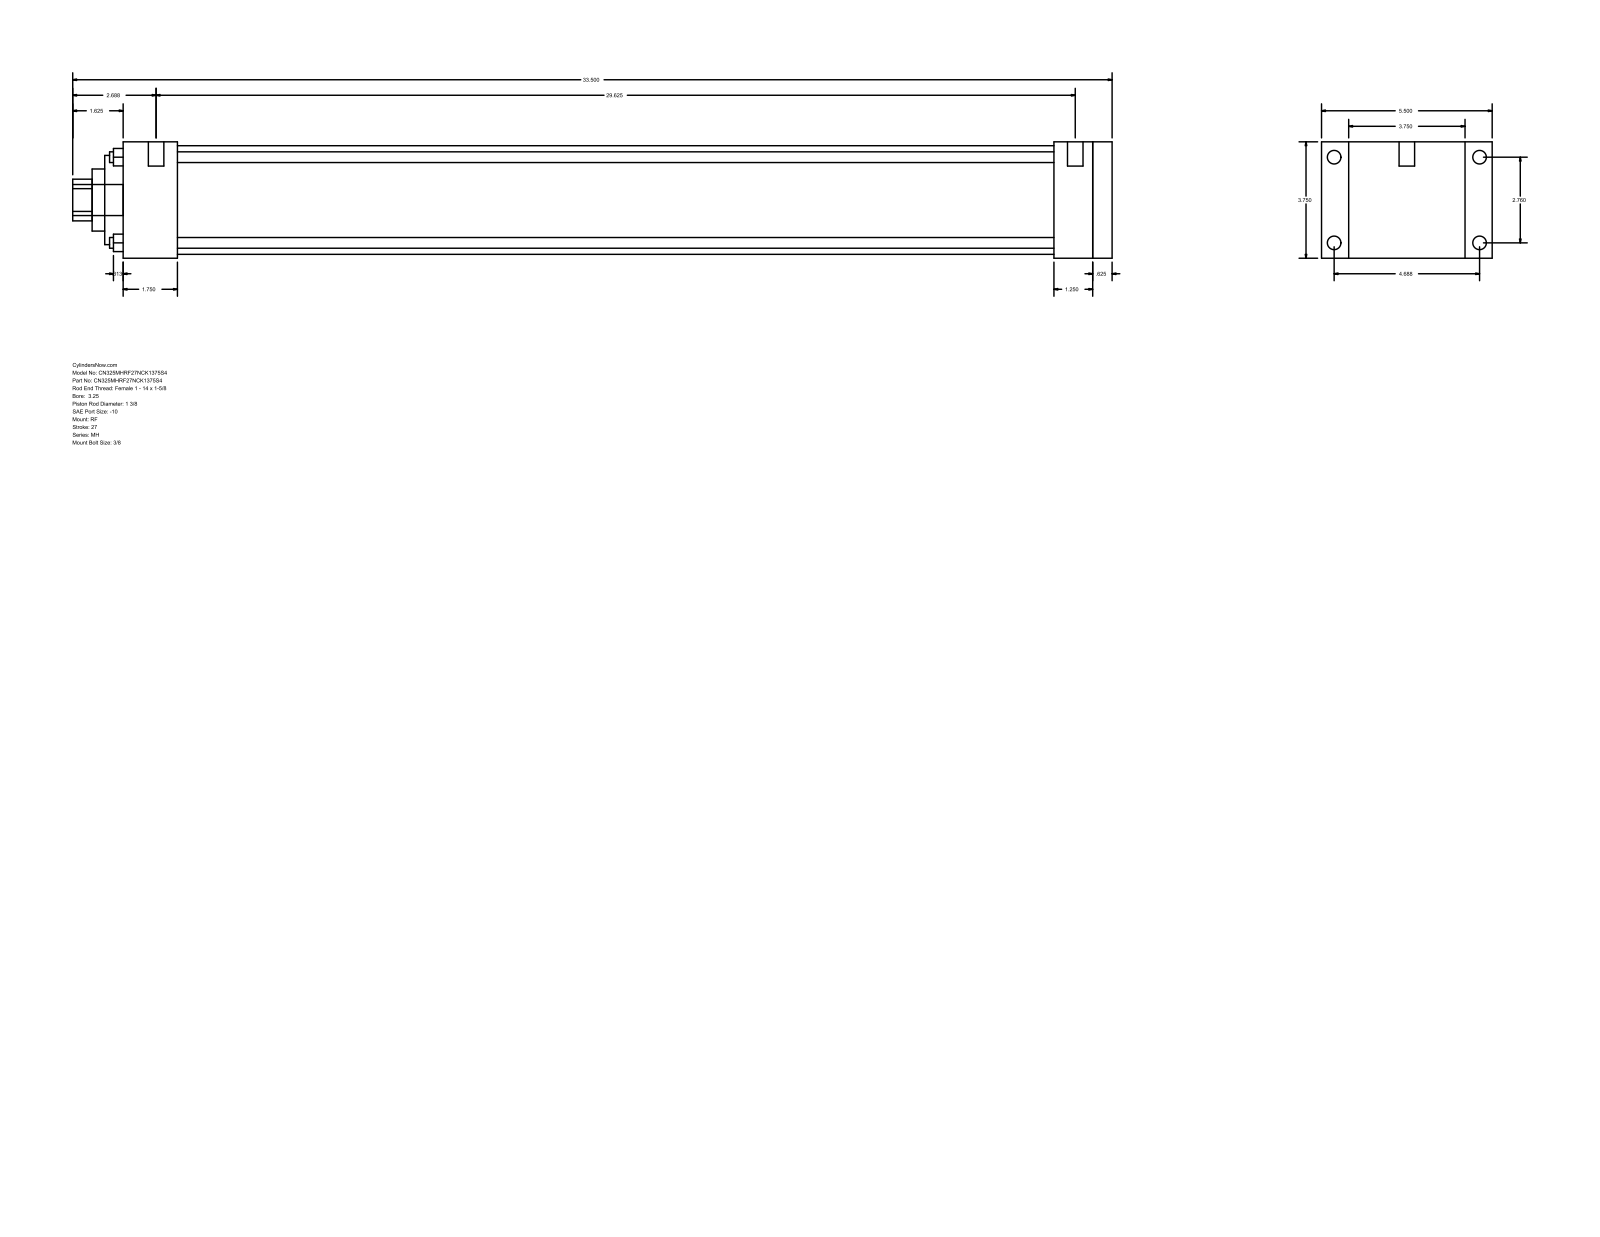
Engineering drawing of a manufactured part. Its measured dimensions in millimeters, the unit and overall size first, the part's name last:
Units: millimetres
Overall size (bounding box): 850.9 × 139.7 × 95.25
Round holes (diameter × count): ⌀8.76 ×4, ⌀34.92 ×1, ⌀50.8 ×1, ⌀73.03 ×1, ⌀88.9 ×1
Round bosses / shafts (diameter × count): ⌀11.13 ×4, ⌀5.56 ×4, ⌀12.7 ×2, ⌀25.4 ×1
Partial cylindrical surfaces — rounded edges, fillets, slot ends (radius × count): R17.06 ×1
Main face-to-face distances: 95.24, 809.63, 15.88, 793.75, 22.23, 117.47, 44.45, 749.3, 765.18, 762
Hole centre spacings: 49.57, 70.1, 99.14
Bodies: 0 solids, 94 faces (65 planar, 29 cylindrical, 0 other)
Part name (STEP PRODUCT): MH_RF__0325_1.375
STEP written by: GSSL Pune (CONFIG_CONTROL_DESIGN)
